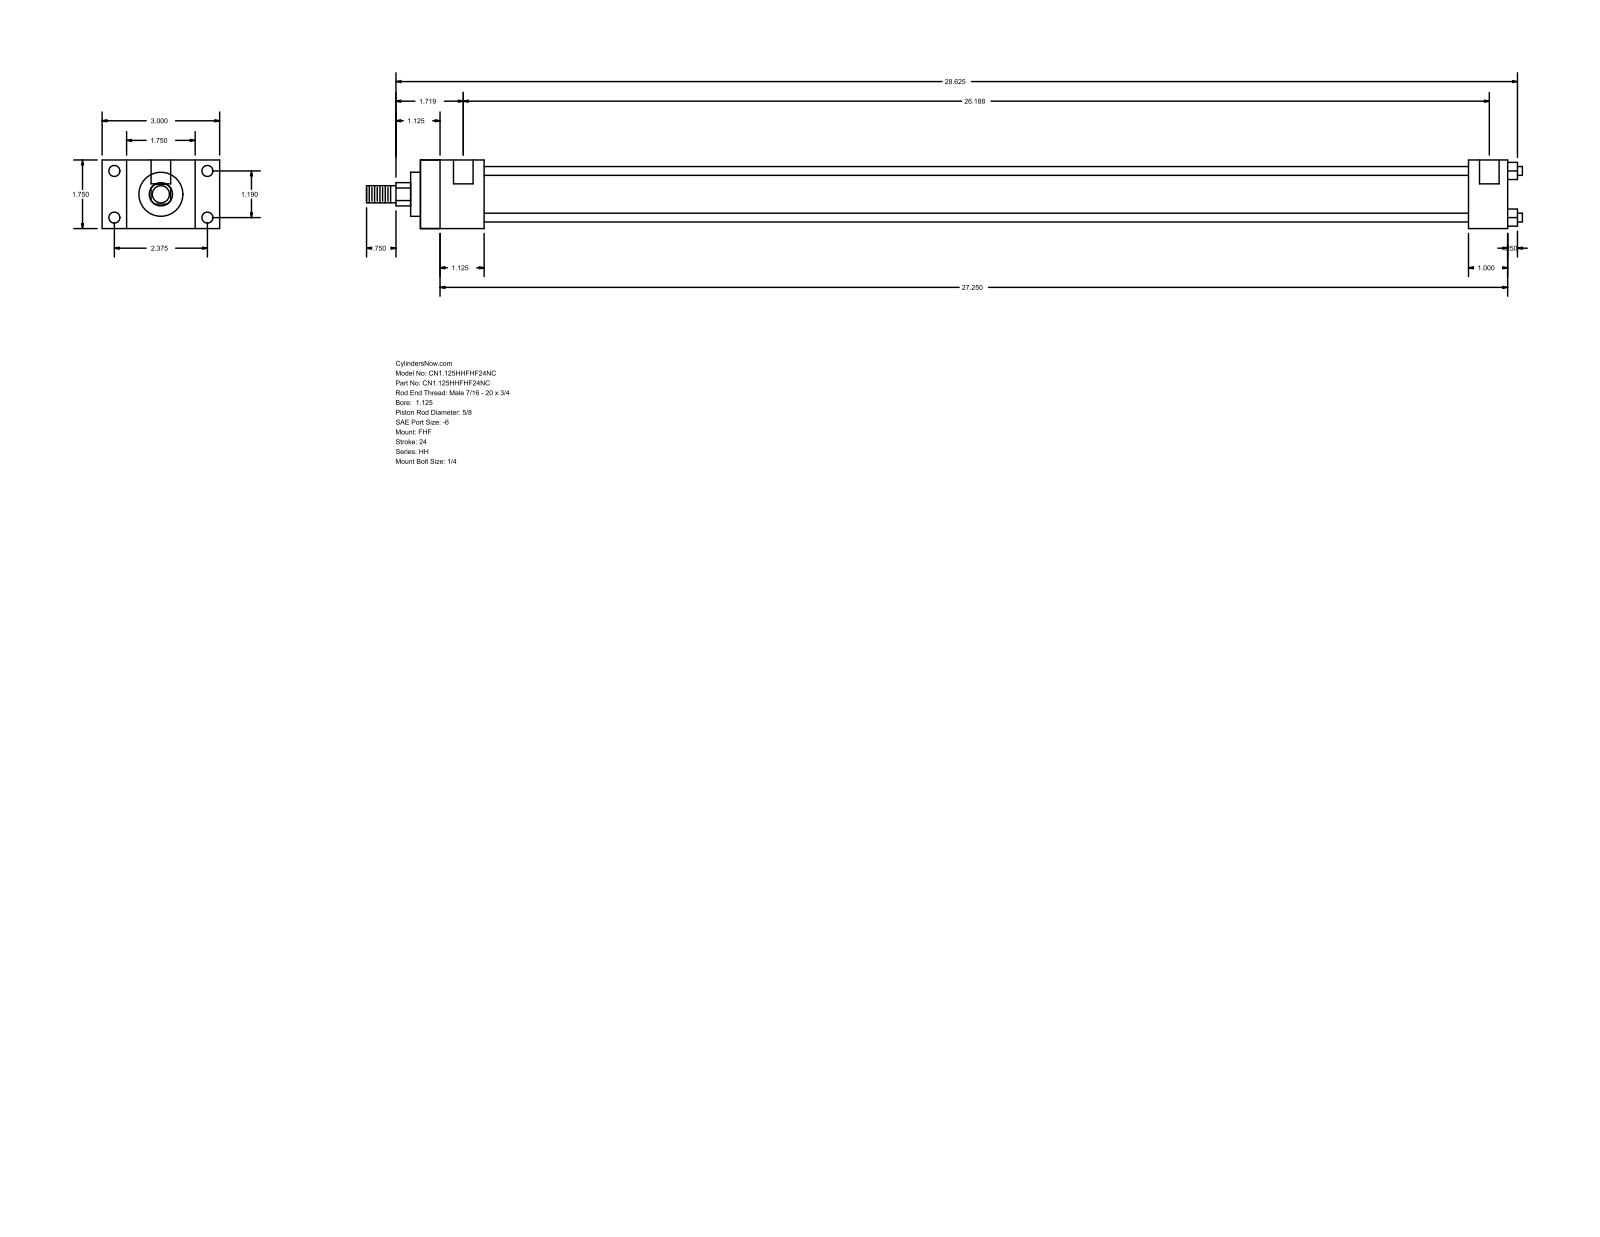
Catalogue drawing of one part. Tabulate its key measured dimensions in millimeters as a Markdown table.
| quantity | value |
| --- | --- |
| part name | HH_FHF__0112_0.625 |
| STEP written by | GSSL Pune (CONFIG_CONTROL_DESIGN) |
| units | millimeters |
| bodies | 0 solids, 88 faces (60 planar, 28 cylindrical, 0 other) |
| overall size | 749.3 × 76.2 × 44.45 |
| round holes (diameter × count) | 5.56 × 4, 7.14 × 4, 12.7 × 2 |
| round bosses / shafts (diameter × count) | 5.71 × 4, 34.92 × 1, 28.57 × 1, 15.88 × 1, 11.11 × 1 |
| partial cylindrical surfaces (radius × count) | 7.54 × 1 |
| main face-to-face distances | 44.46, 15.87, 60.33, 41.27, 76.2, 704.85, 663.58, 25.4, 679.45, 638.18 |
| hole center spacings | 30.22, 60.32, 67.47, 661.99, 3.17, 665.16 |
